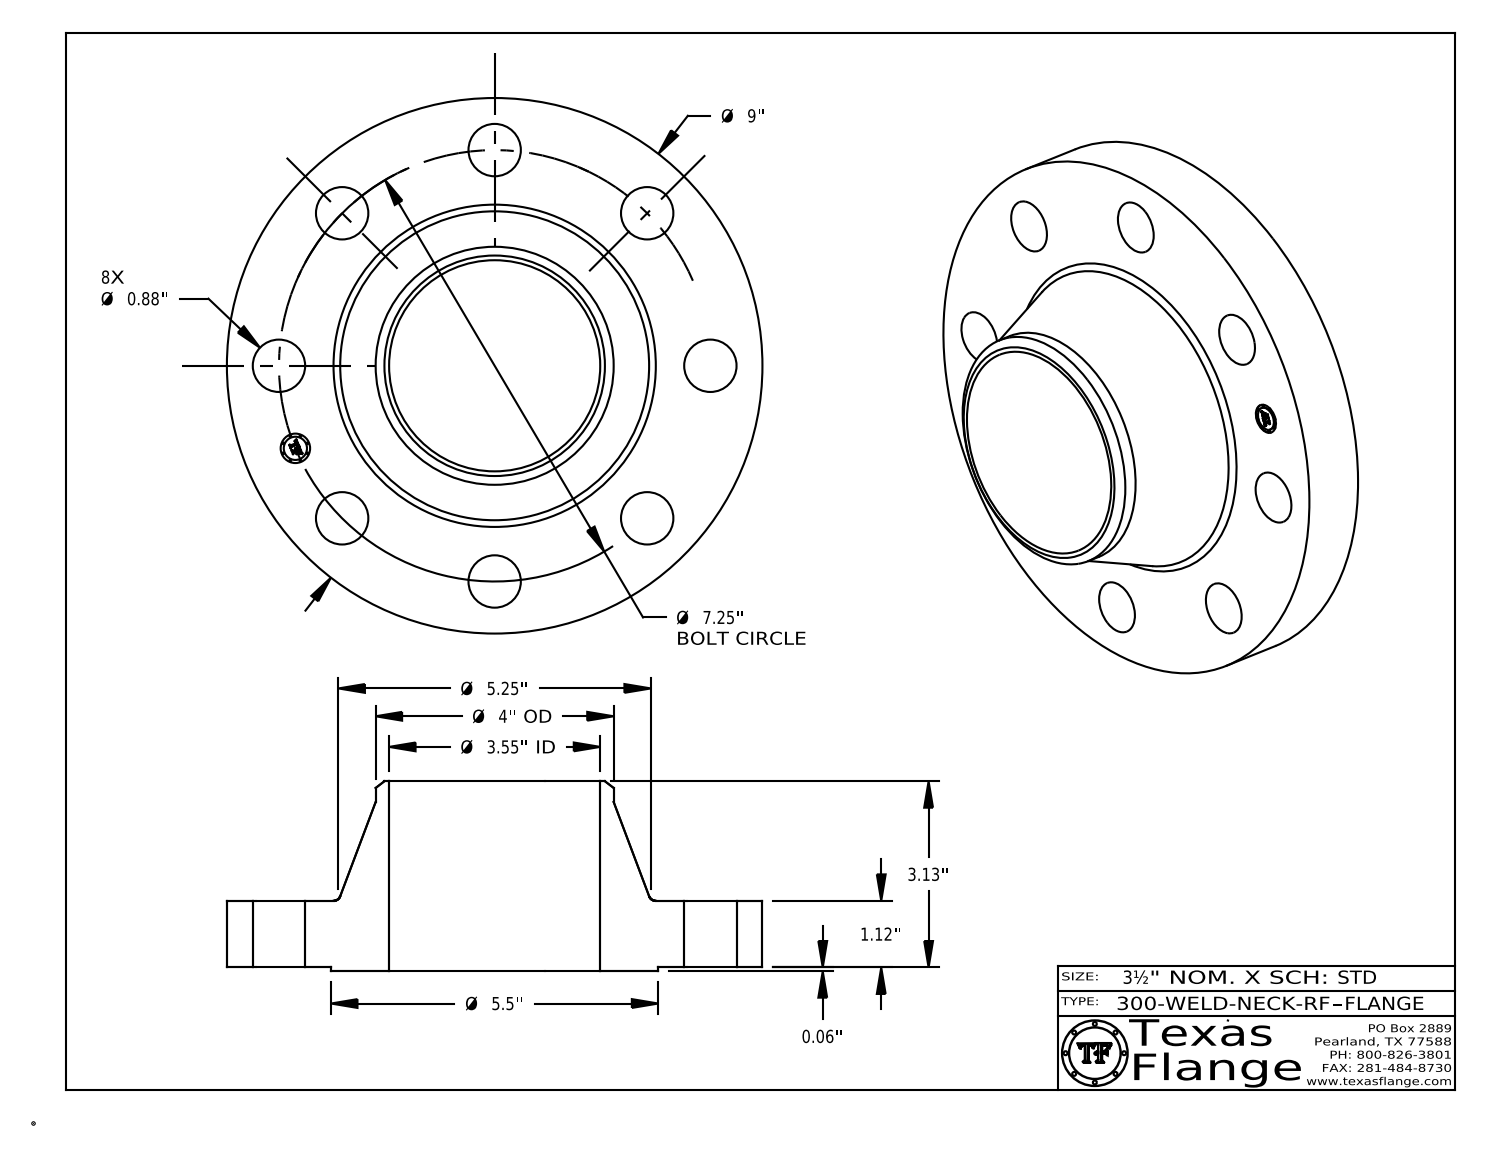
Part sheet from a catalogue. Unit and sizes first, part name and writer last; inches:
Units: inches
Overall size (bounding box): 9 × 9 × 3.193
Round holes (diameter × count): ⌀0.88 ×8, ⌀0.495 ×1, ⌀3.548 ×1
Round bosses / shafts (diameter × count): ⌀0.03 ×8, ⌀9 ×1, ⌀5.5 ×1, ⌀4 ×1, ⌀0.39 ×1
Main face-to-face distances: 1.12, 0.063, 1.183, 3.193, 3.13, 2.01, 1.168, 1.105, 0.015, 2.025
Hole centre spacings: 3.625, 2.774, 5.127, 6.698, 7.25, 1.415, 7.111, 4.028
Volume: 68.1 in³ · Surface area: 210.7 in²
Bodies: 1 solid, 419 faces (369 planar, 44 cylindrical, 6 other)
Part name (STEP PRODUCT): 300-WELD-NECK-RF
STEP written by: CATIA V5 STEP AP214 (AUTOMOTIVE_DESIGN)
